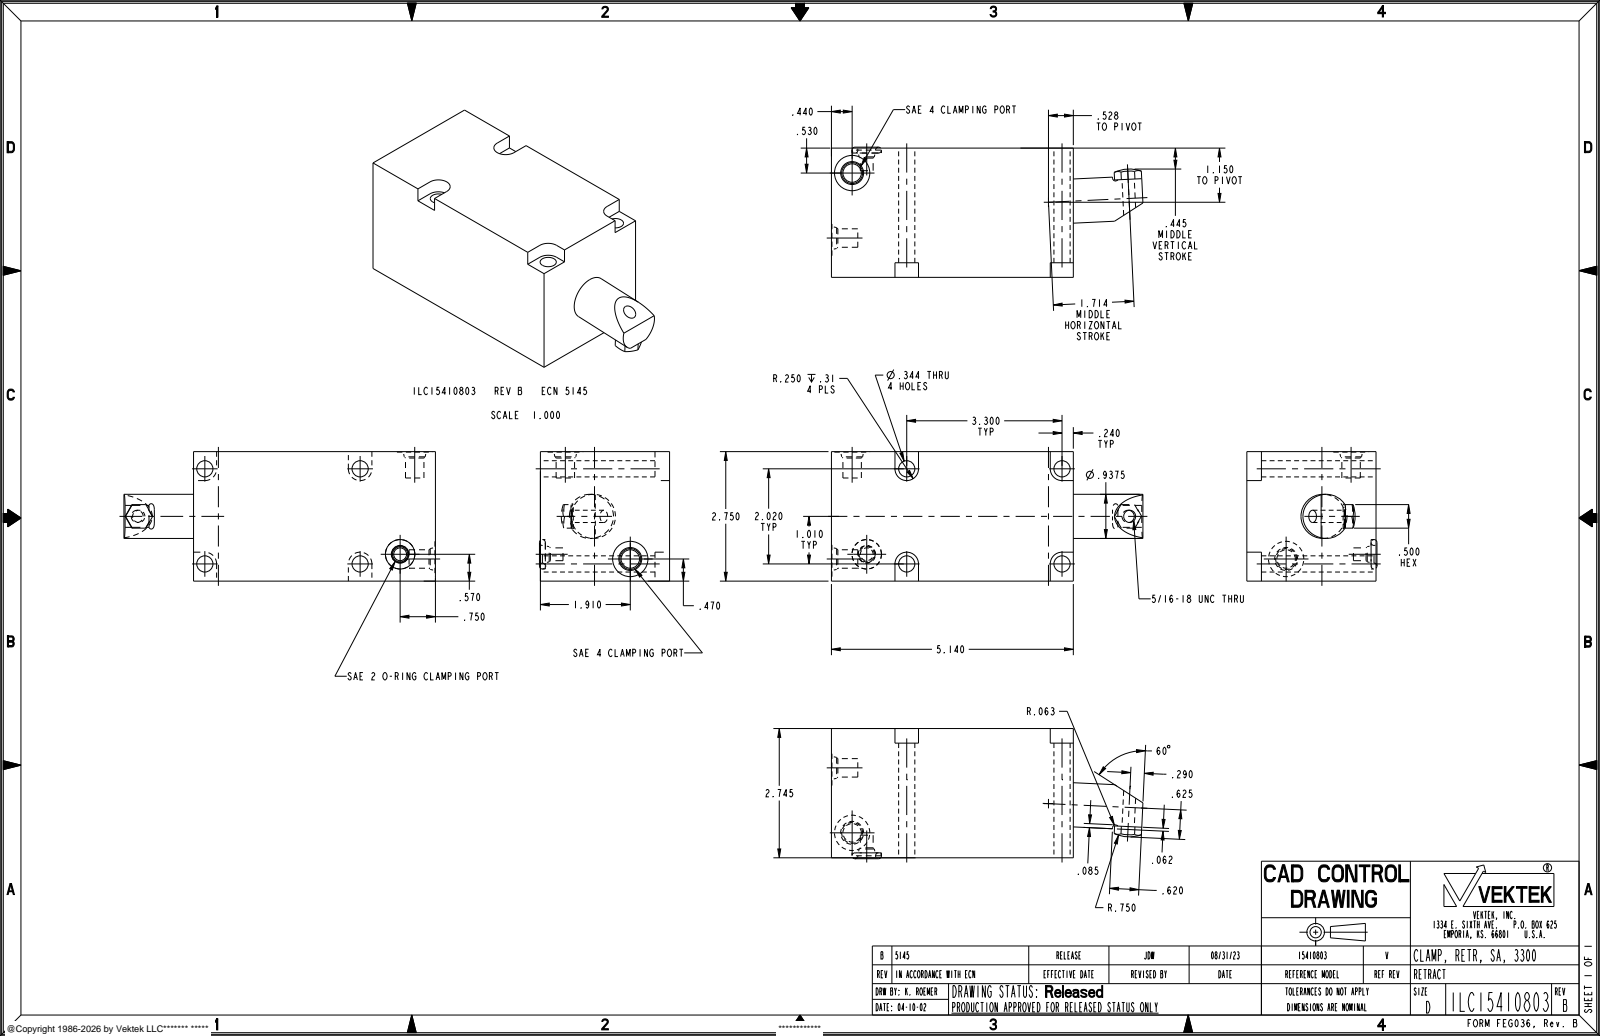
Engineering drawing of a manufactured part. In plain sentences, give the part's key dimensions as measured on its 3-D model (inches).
The part is named "ILC15410803". Its 3-D file was written by "CREO PARAMETRIC BY PTC INC, 2021164 (AUTOMOTIVE_DESIGN)". It is 1 solid with 88 faces: 40 planar, 30 cylindrical and 18 other. Overall it measures 6.619 by 2.765 by 2.75 inches. Its volume is 38.3 cubic inches and its surface area 89.39 square inches. Round holes: 4 of diameter 0.344, 2 of diameter 0.392, 2 of diameter 0.75, 1 of diameter 0.261, 1 of diameter 0.272, 1 of diameter 0.625. Round bosses or shafts: 1 of diameter 0.937. Partial cylindrical surfaces (rounded edges, fillets, slot ends): 4 of radius 0.25, 1 of radius 0.063. The main face-to-face distances are 2.75, 2.745, 5.14, 2.435, 0.31, 0.5, 2.74, 5.13, 0.55, 1.35. The hole center spacings are 2.02, 3.3, 3.869, 0.874, 2.004, 4.155, 4.53.
